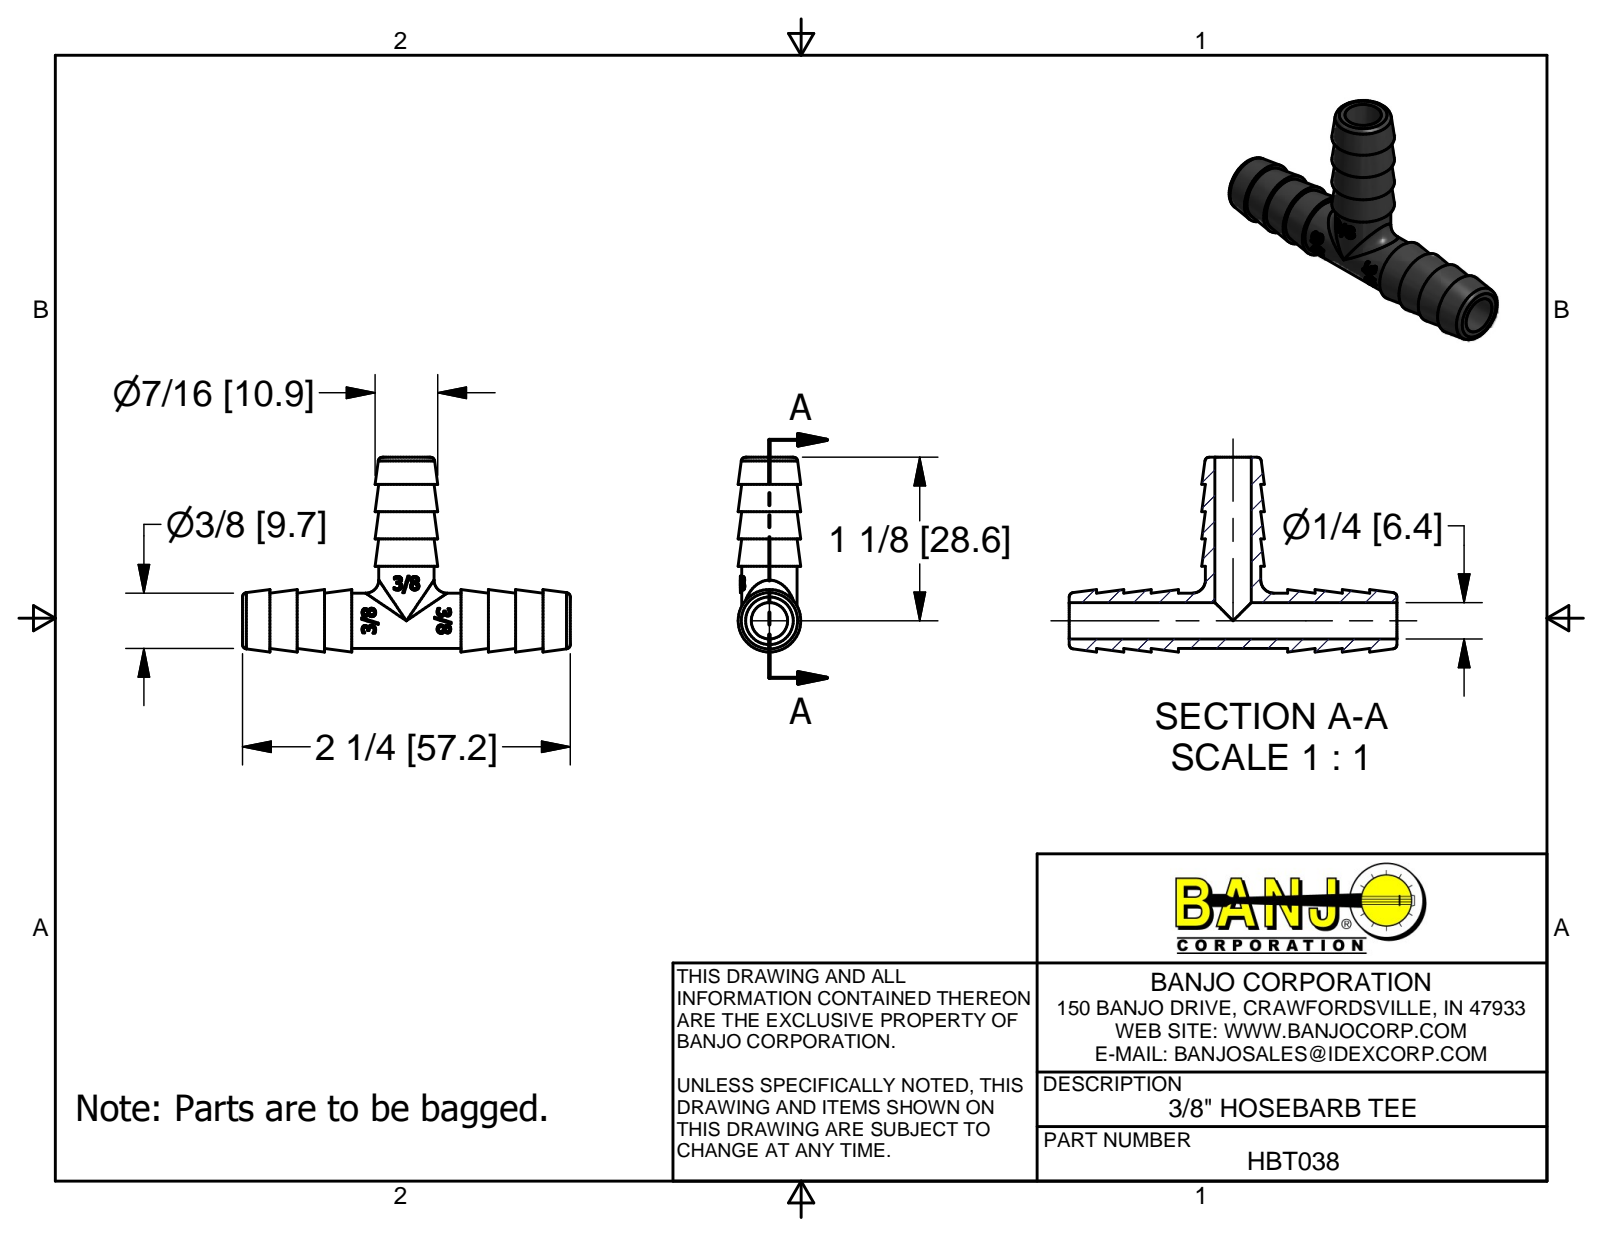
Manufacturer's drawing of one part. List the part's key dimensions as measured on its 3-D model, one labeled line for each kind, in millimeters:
Part name (STEP PRODUCT): HBT038
STEP written by: Autodesk Inventor 2013 (AUTOMOTIVE_DESIGN)
Units: millimetres
Bodies: 1 solid, 207 faces (57 planar, 19 cylindrical, 131 other)
Overall size (bounding box): 57.2 × 34 × 10.9
Volume: 3 930 mm³ · Surface area: 4 536 mm²
Round holes (diameter × count): ⌀6.4 ×2
Round bosses / shafts (diameter × count): ⌀9.7 ×2
Partial cylindrical surfaces — rounded edges, fillets, slot ends (radius × count): R5.1 ×2
Main face-to-face distances: 4.7, 9.5, 33.4, 14.3, 19.1, 14.3, 9.5, 4.8, 38.1, 28.6
